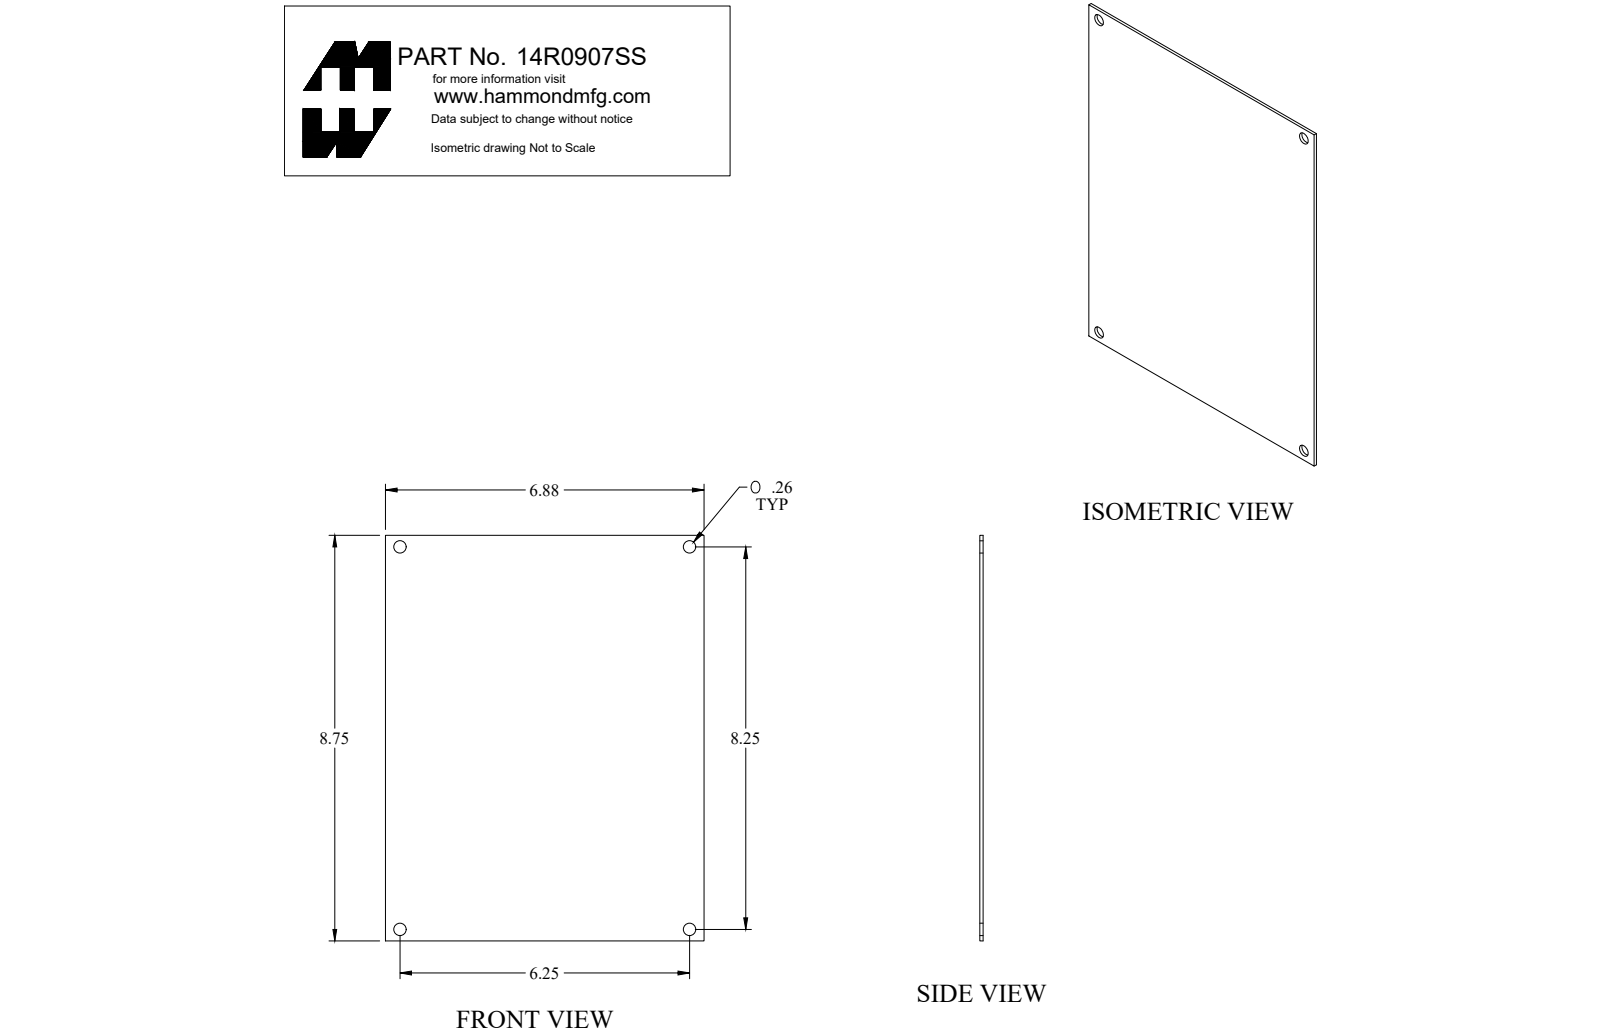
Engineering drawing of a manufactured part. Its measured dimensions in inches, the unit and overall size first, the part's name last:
Units: inches
Overall size (bounding box): 8.75 × 6.875 × 0.072
Round holes (diameter × count): ⌀0.265 ×4
Main face-to-face distances: 0.072, 6.875, 8.75
Hole centre spacings: 6.25, 8.25, 10.35
Volume: 4.315 in³ · Surface area: 122.4 in²
Bodies: 1 solid, 10 faces (6 planar, 4 cylindrical, 0 other)
Part name (STEP PRODUCT): 14R0907SS
STEP written by: SolidWorks 2018 (AUTOMOTIVE_DESIGN)
